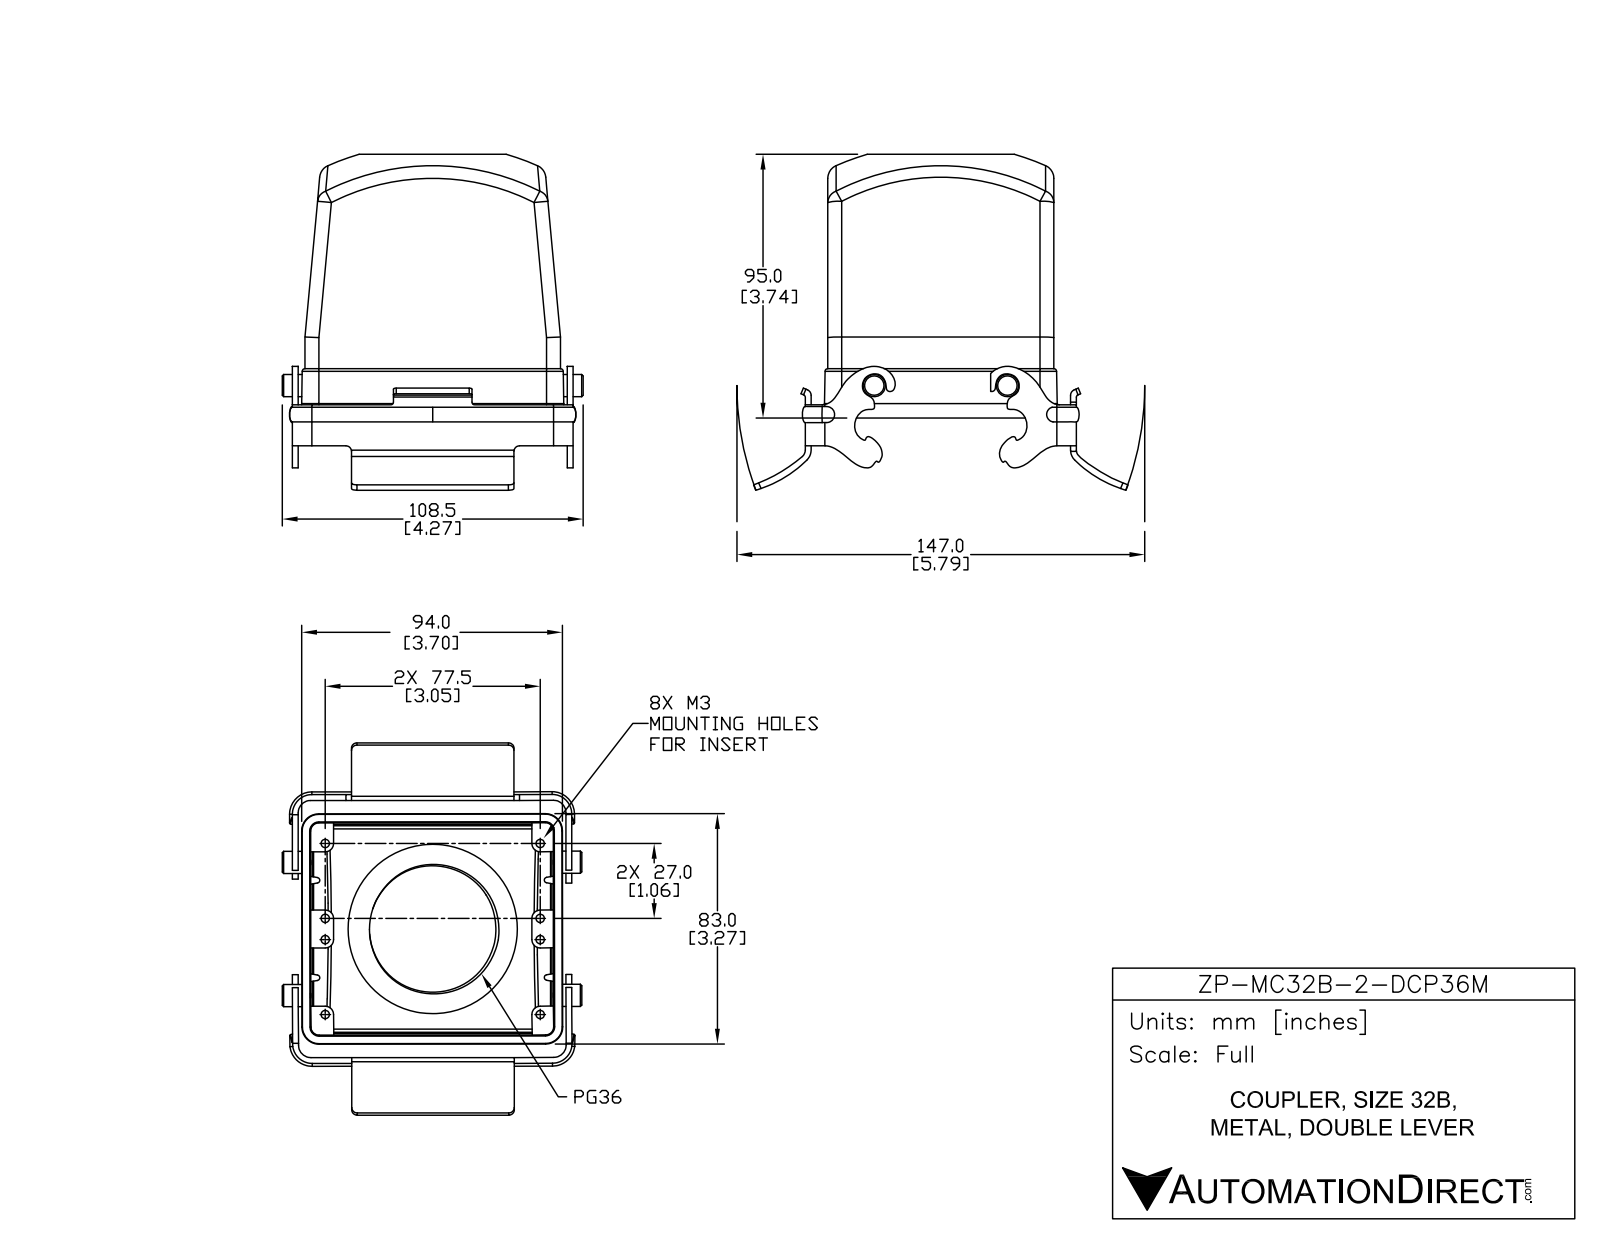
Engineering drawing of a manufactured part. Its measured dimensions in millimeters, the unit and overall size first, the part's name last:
Units: millimetres
Overall size (bounding box): 135.05 × 123.97 × 108.45
Round holes (diameter × count): ⌀3 ×8, ⌀1.78 ×2, ⌀45.6 ×1, ⌀53 ×1
Round bosses / shafts (diameter × count): ⌀7.98 ×2, ⌀61 ×1
Partial cylindrical surfaces — rounded edges, fillets, slot ends (radius × count): R1 ×14, R3 ×10, R5 ×10, R2 ×6, R0.5 ×4, R4.5 ×4, R7.05 ×4, R1.42 ×2
Main face-to-face distances: 3.1, 78.4, 81.5, 75.3, 2.1, 6.02, 9.12, 84.42, 87.52, 8.12
Hole centre spacings: 27, 34.64, 38.94, 49.51, 77.5, 82.07, 84.89, 7.64
Volume: 150 437 mm³ · Surface area: 93 031 mm²
Bodies: 4 solids, 373 faces (158 planar, 124 cylindrical, 91 other)
Part name (STEP PRODUCT): ZP-MC32B-2-DCP36M
STEP written by: SolidWorks 2014 (AUTOMOTIVE_DESIGN)
